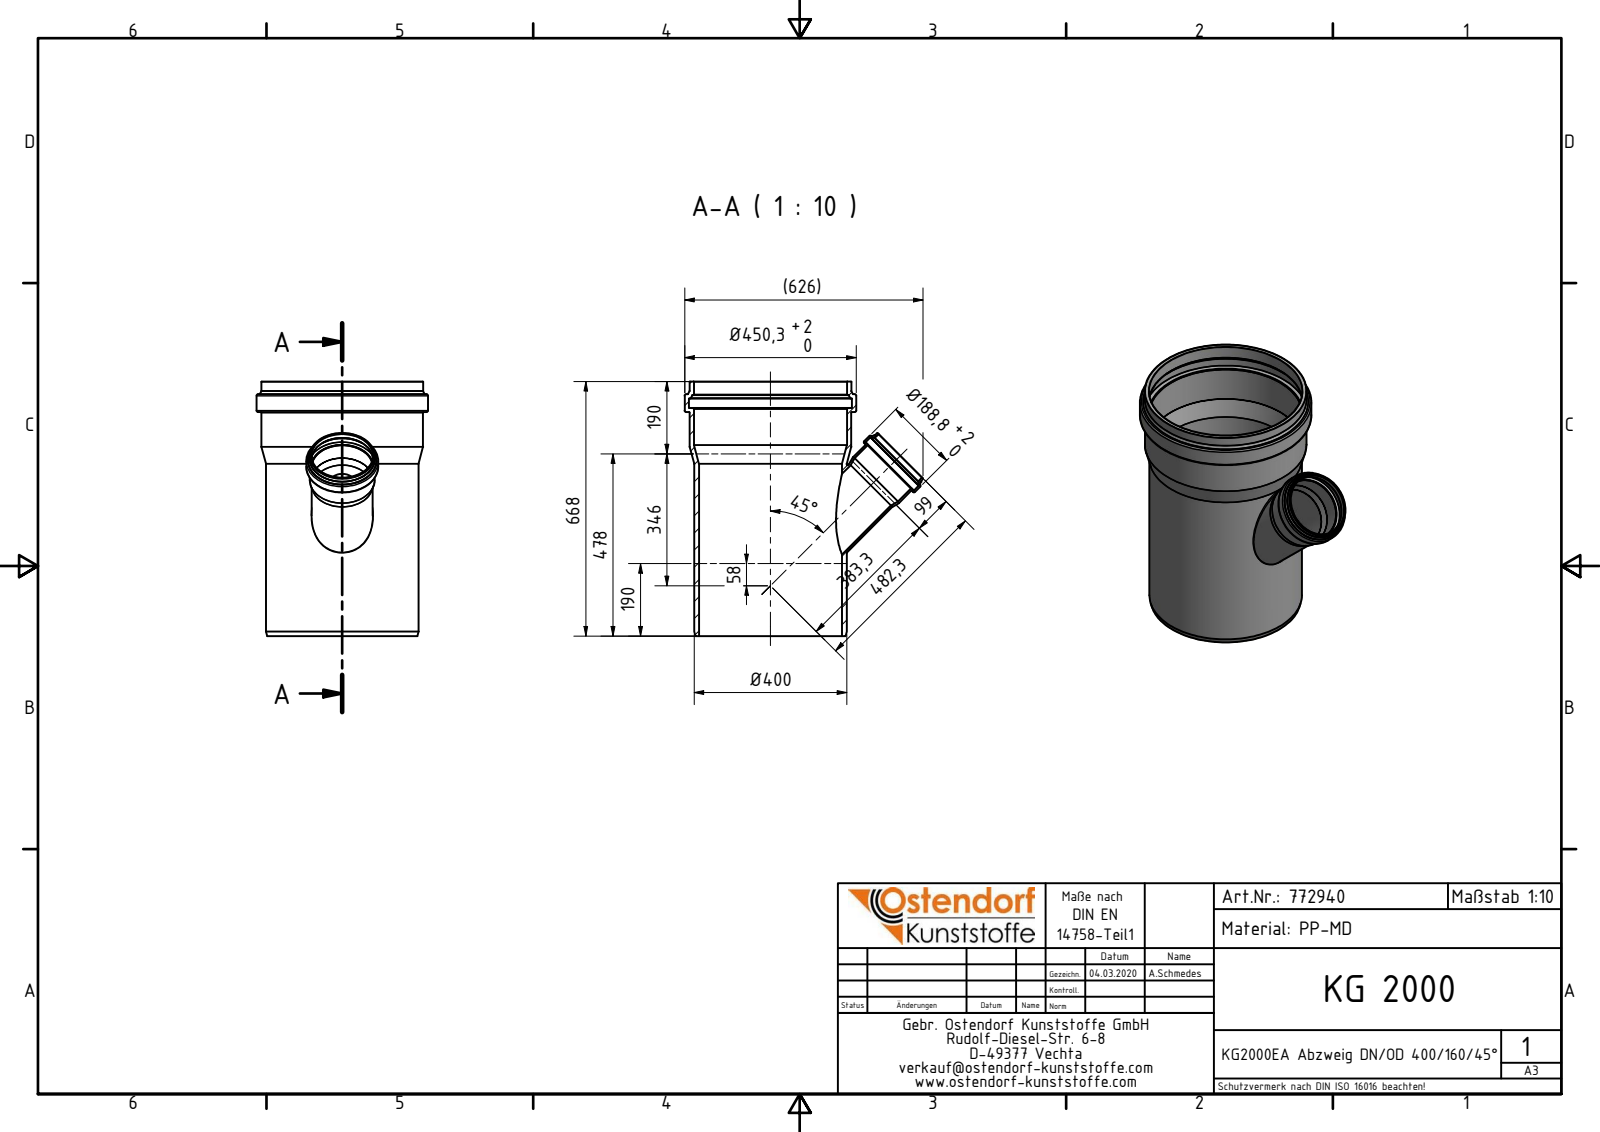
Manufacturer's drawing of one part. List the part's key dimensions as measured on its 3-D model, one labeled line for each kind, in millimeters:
Part name (STEP PRODUCT): 772940 KG2000EA Abzweig DN_OD 400_160_45°
STEP written by: Autodesk Inventor 2020 (AUTOMOTIVE_DESIGN)
Units: millimetres
Bodies: 1 solid, 79 faces (10 planar, 18 cylindrical, 51 other)
Overall size (bounding box): 668 × 626 × 450.3
Volume: 10 680 000 mm³ · Surface area: 1 929 000 mm²
Round holes (diameter × count): ⌀161 ×2, ⌀149.7 ×1, ⌀160.7 ×1, ⌀179.4 ×1, ⌀375.5 ×1, ⌀401.7 ×1, ⌀402.1 ×1, ⌀427.7 ×1
Round bosses / shafts (diameter × count): ⌀450.3 ×1, ⌀424.7 ×1, ⌀424.3 ×1, ⌀400.5 ×1, ⌀188.8 ×1, ⌀170.4 ×1, ⌀170.3 ×1, ⌀160.1 ×1
Main face-to-face distances: 668, 587.6, 80.4, 33.4, 634.6, 47, 43.69, 26.7, 16.99, 595.74
